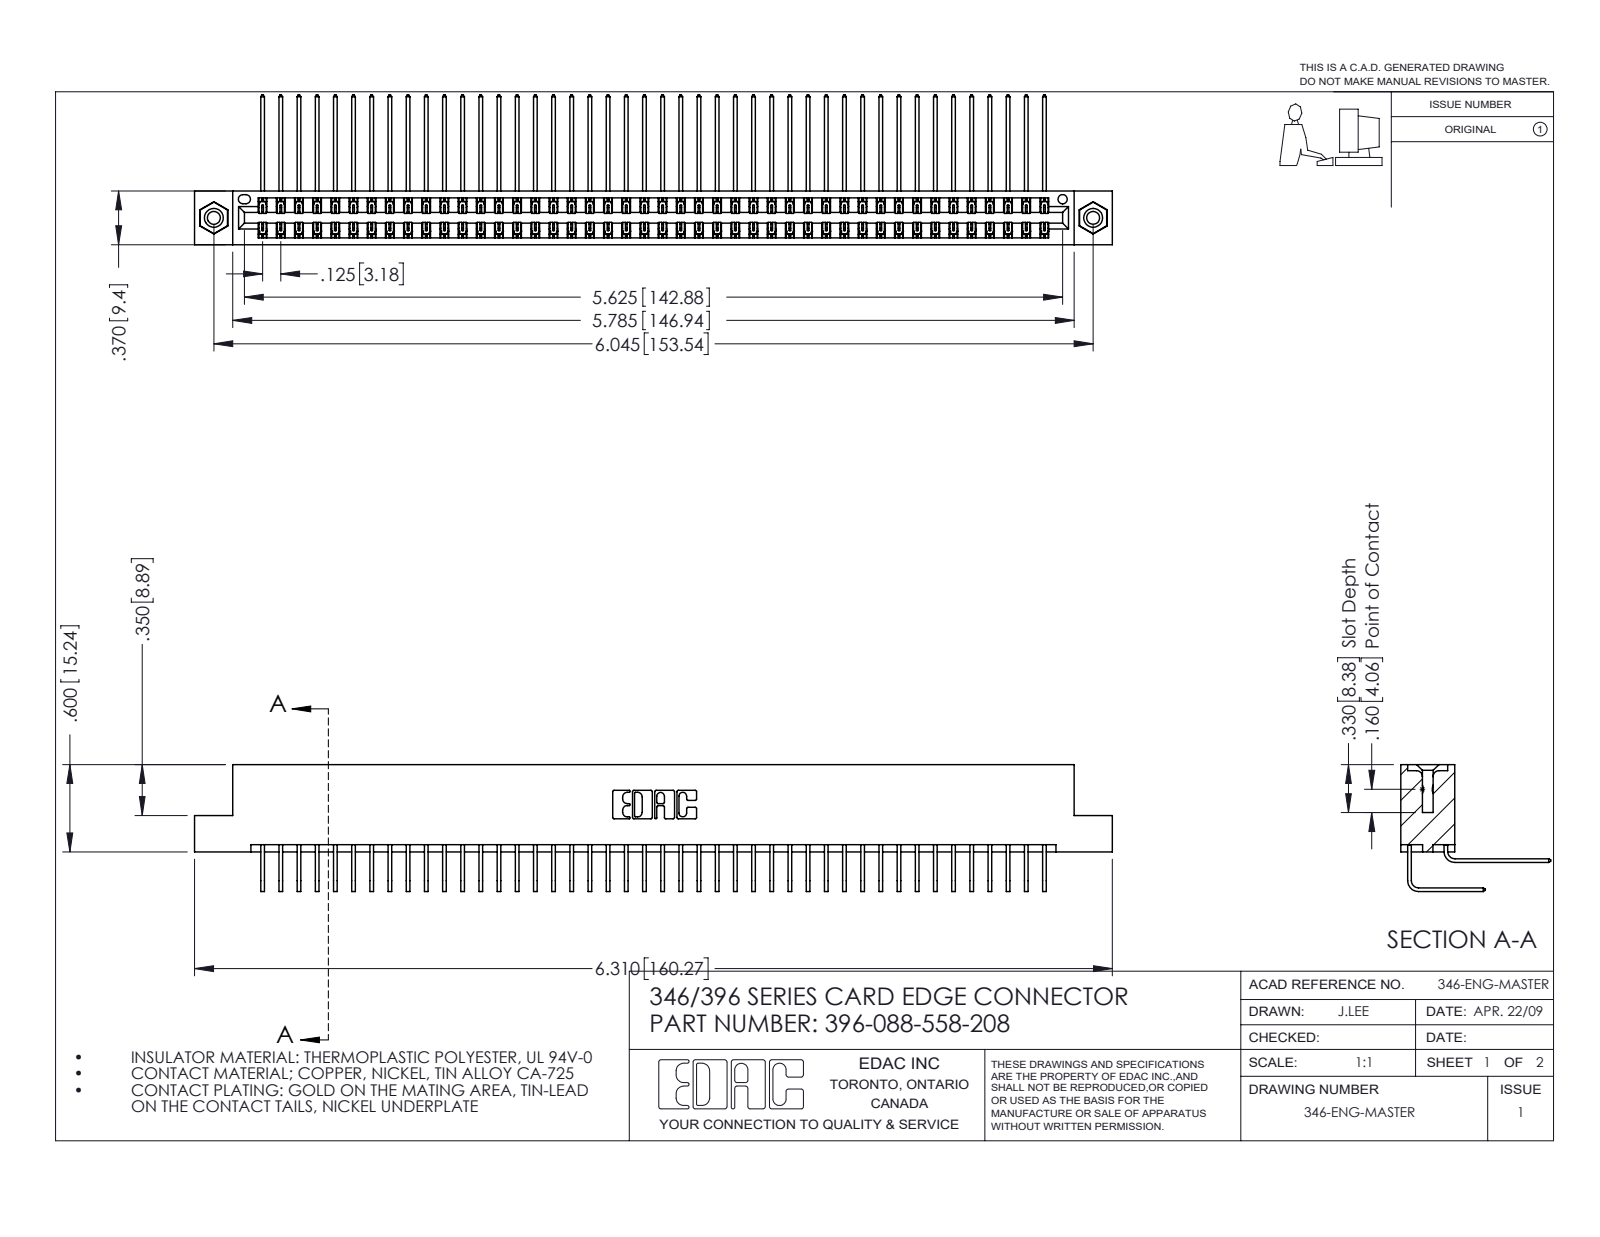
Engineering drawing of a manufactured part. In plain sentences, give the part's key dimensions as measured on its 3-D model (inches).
The part is named "345-292-001_558 559 Tail - 1; 396-088-558-208; 346 Part_Flush Mounting Lugs - 0.156 Dia-TI; 345-292-001_558 Tail - 2 (+1 more)". Its 3-D file was written by "SolidWorks 2016 (CONFIG_CONTROL_DESIGN)". It is 91 solids with 4934 faces: 3364 planar, 1554 cylindrical and 16 other. Overall it measures 6.31 by 1.03 by 0.873 inches. Its volume is 0.985 cubic inches and its surface area 38.25 square inches. Round holes: 2 of diameter 0.089, 2 of diameter 0.125, 2 of diameter 0.156, 1 of diameter 0.064. Round bosses or shafts: 2 of diameter 0.155. Partial cylindrical surfaces (rounded edges, fillets, slot ends): 132 of radius 0.006, 22 of radius 0.01, 6 of radius 0.007, 6 of radius 0.031, 3 of radius 0.026, 2 of radius 0.014, 2 of radius 0.022, 2 of radius 0.024. The main face-to-face distances are 0.048, 0.322, 0.025, 0.37, 0.25, 0.072, 0.298, 0.275, 0.148, 0.222. The hole center spacings are 0.246, 5.836, 6.045.
